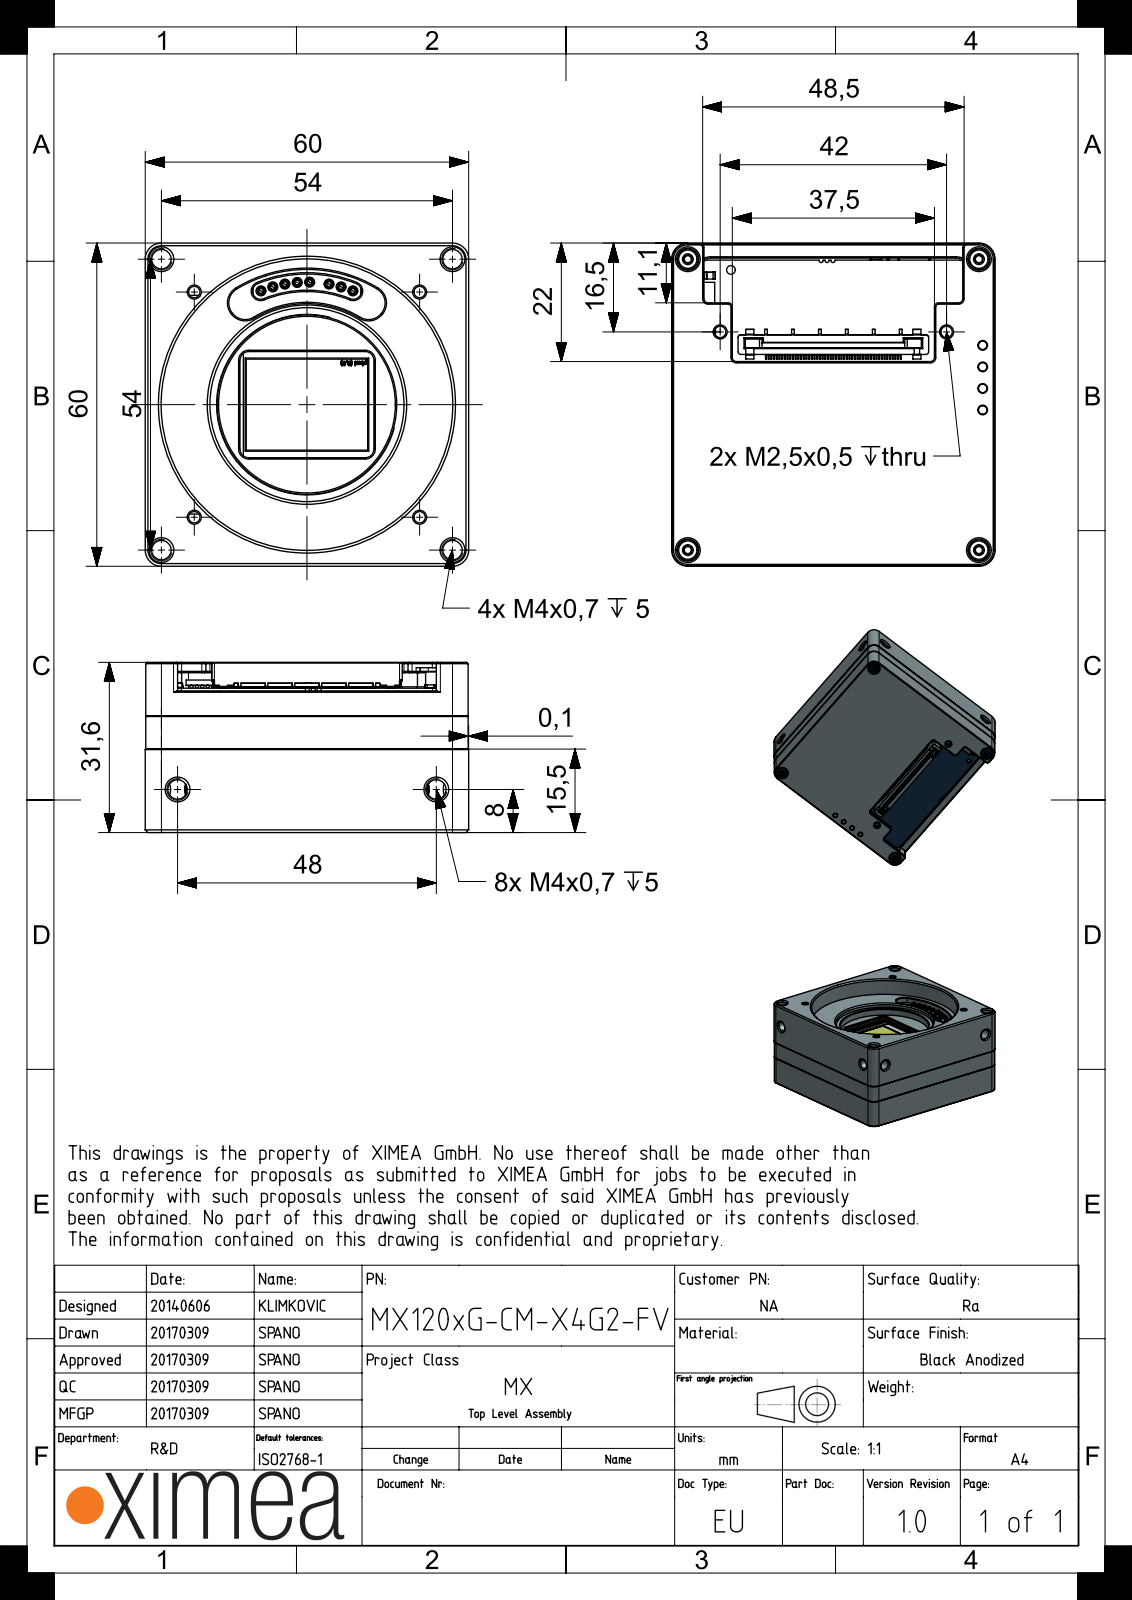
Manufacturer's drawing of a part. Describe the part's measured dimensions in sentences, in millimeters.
The part is named "MX-X4G2-MAIN-FV-LIGHTWEIGHT; MECH-GASKET-CB120; SROB-M2X20-IMBUS-STNLS; MECH-MX200-REAR (+8 more)". Its 3-D file was written by "SIEMENS PLM Software NX 11.0 (AUTOMOTIVE_DESIGN)". It is 38 solids with 5076 faces: 2999 planar, 1430 cylindrical and 647 other. Overall it measures 60 by 60 by 31.6 millimeters. Its volume is 45 410 cubic millimeters and its surface area 55 450 square millimeters. Round holes: 20 of diameter 1.6, 14 of diameter 2.1, 9 of diameter 1.3, 8 of diameter 0.9, 8 of diameter 1.1, 8 of diameter 1.3, 8 of diameter 3.6, 6 of diameter 2, 4 of diameter 0.7, 4 of diameter 0.9, 4 of diameter 4, 4 of diameter 4.1. Round bosses or shafts: 237 of diameter 0.3, 8 of diameter 1.8, 8 of diameter 1.5, 8 of diameter 1.5, 8 of diameter 1.2, 8 of diameter 1.1, 4 of diameter 3.8, 4 of diameter 3. Partial cylindrical surfaces (rounded edges, fillets, slot ends): 52 of radius 0.5, 44 of radius 1.5, 38 of radius 0.2, 35 of radius 3, 24 of radius 0.1, 18 of radius 0.6, 14 of radius 0.8, 12 of radius 1. The main face-to-face distances are 1, 4.7, 11.6, 10.6, 9.5, 12.1, 10.5, 59.9, 2.6, 21.1. The hole center spacings are 48.3, 2.3, 8.6, 22.8, 22.8, 29.6, 38.2, 41.8.
